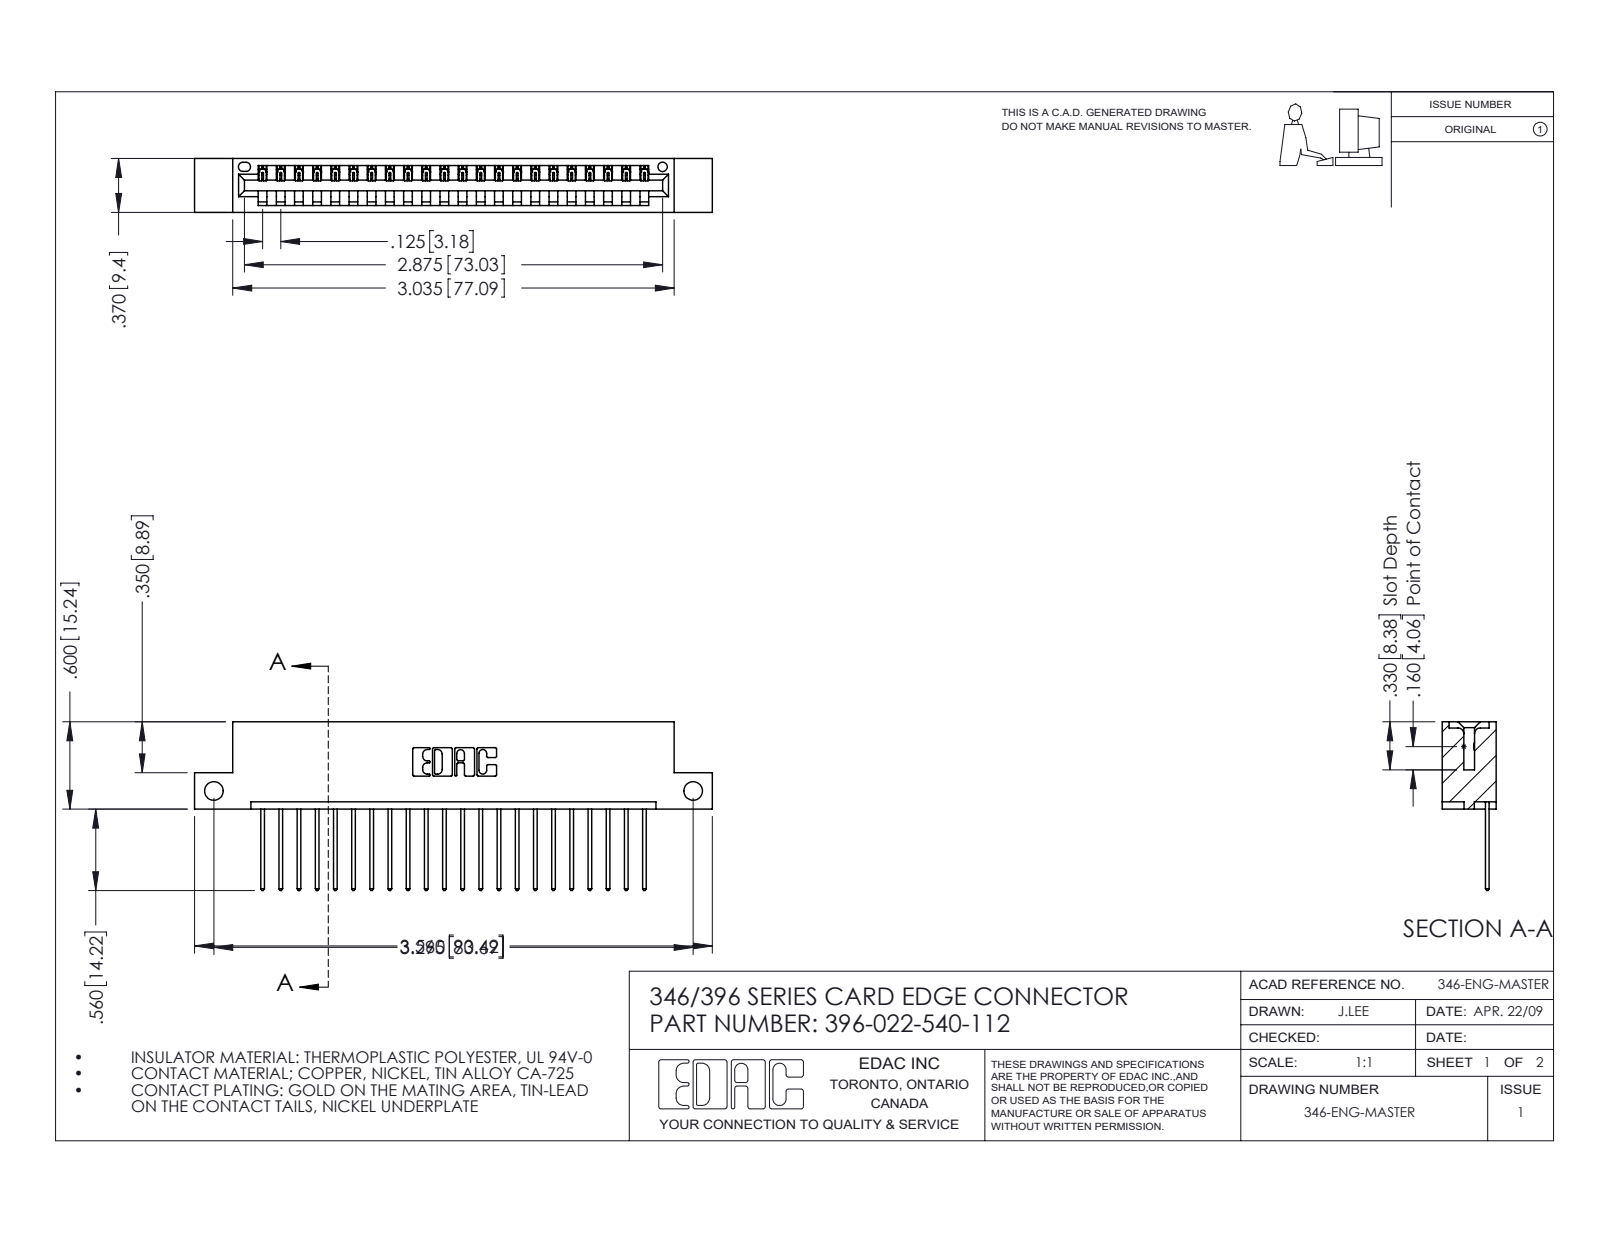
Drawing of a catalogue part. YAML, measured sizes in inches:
part_name: "345-292-001_345-293-140; 346 Part_Flush Mounting Lugs - Side Mount; 396-022-540-112"
step_written_by: "SolidWorks 2016 (CONFIG_CONTROL_DESIGN)"
units: inches
bodies: {solids: 23, faces: 1398, planar: 956, cylindrical: 442, other: 0}
overall_size: [3.56, 1.16, 0.37]
volume: 0.516
surface_area: 16.17
round_holes:
  - {diameter: 0.128, count: 2}
  - {diameter: 0.064, count: 1}
partial_cylinders:
  - {radius: 0.006, count: 44}
  - {radius: 0.01, count: 44}
  - {radius: 0.01, count: 22}
  - {radius: 0.007, count: 6}
  - {radius: 0.031, count: 6}
  - {radius: 0.026, count: 3}
  - {radius: 0.031, count: 2}
  - {radius: 0.04, count: 2}
face_to_face_distances: [0.048, 0.322, 0.25, 0.37, 0.072, 0.298, 0.025, 0.148, 0.222, 0.1]
hole_center_spacings: [3.295]
